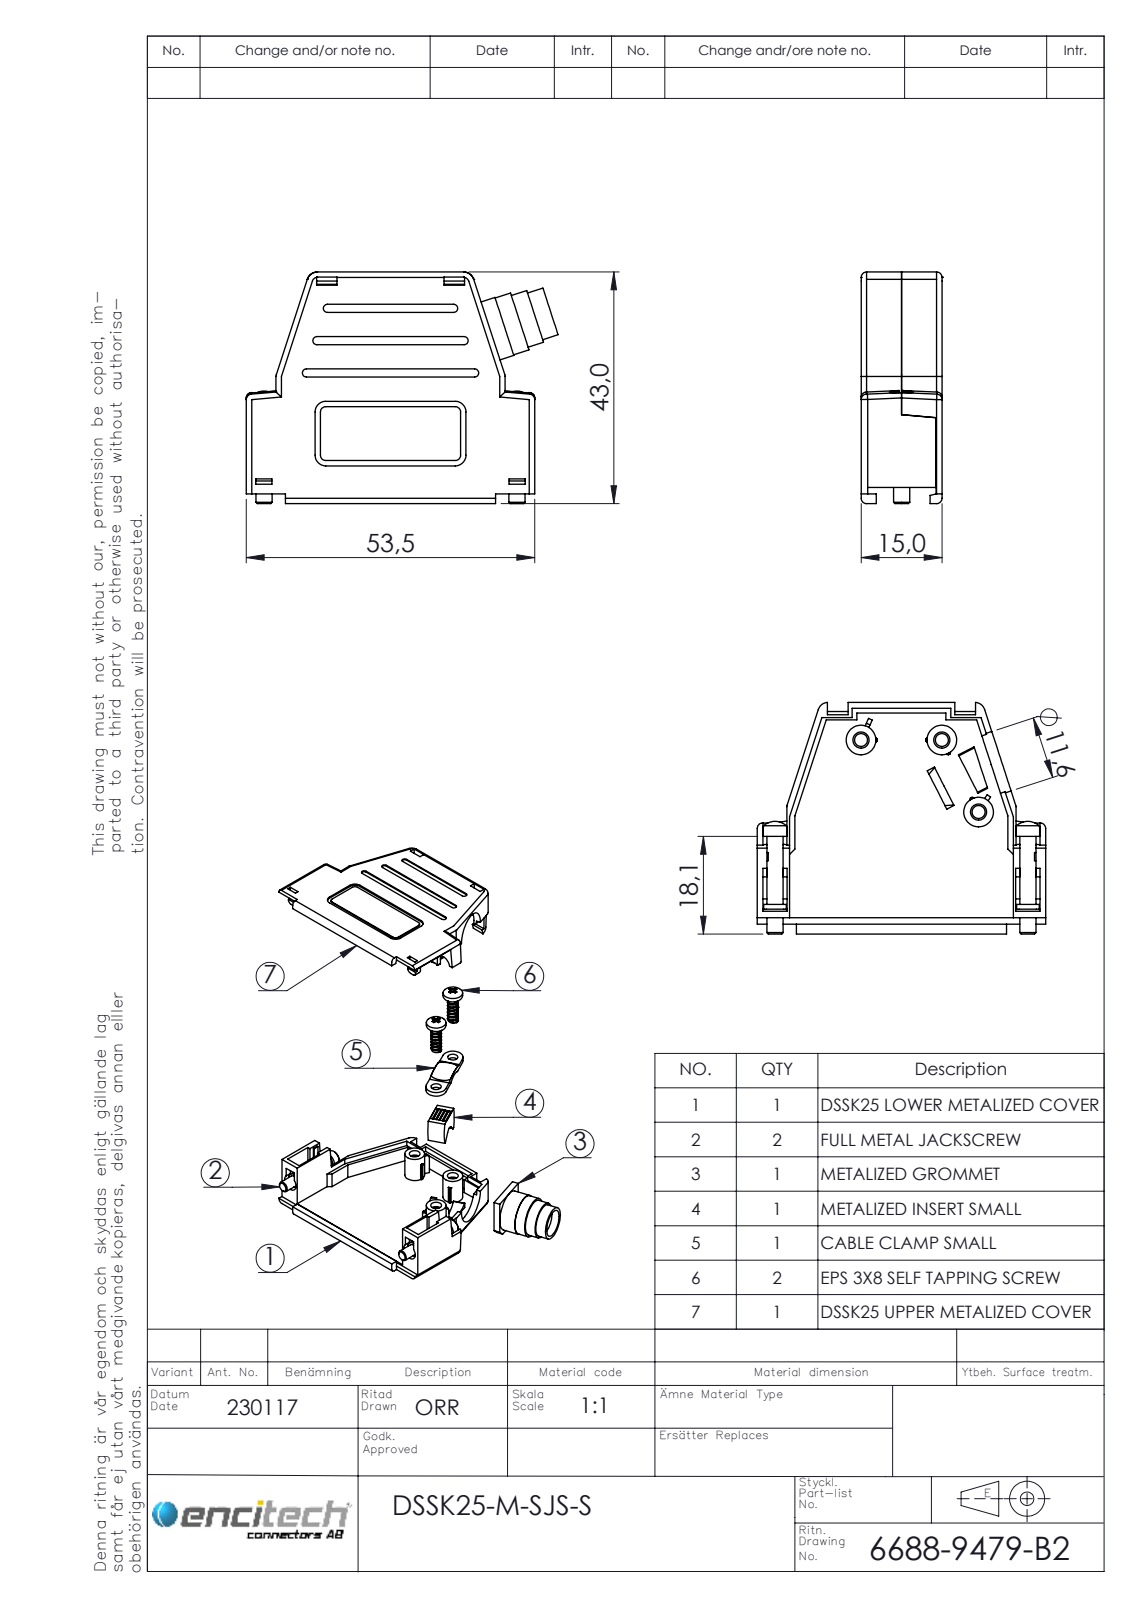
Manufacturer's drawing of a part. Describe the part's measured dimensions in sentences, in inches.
The part is named "6838-0109-32; 6826-0133-01; 6855-0109-01; 6811-0132-05 Part 1 (+4 more)". Its 3-D file was written by "SolidWorks 2021 (AUTOMOTIVE_DESIGN)". It is 11 solids with 758 faces: 482 planar, 216 cylindrical and 60 other. Overall it measures 2.277 by 1.693 by 0.591 inches. Its volume is 0.652 cubic inches and its surface area 24.68 square inches. Round holes: 3 of diameter 0.094, 3 of diameter 0.118, 2 of diameter 0.11, 1 of diameter 0.138, 1 of diameter 0.295, 1 of diameter 0.335, 1 of diameter 0.374, 1 of diameter 0.413, 1 of diameter 0.457. Round bosses or shafts: 3 of diameter 0.217, 2 of diameter 0.215, 2 of diameter 0.173, 2 of diameter 0.165, 2 of diameter 0.118, 2 of diameter 0.097, 1 of diameter 0.445, 1 of diameter 0.437. Partial cylindrical surfaces (rounded edges, fillets, slot ends): 40 of radius 0.039, 14 of radius 0.079, 6 of radius 0.03, 4 of radius 0.004, 4 of radius 0.01, 4 of radius 0.02, 3 of radius 0.228, 2 of radius 0.047. The main face-to-face distances are 0.524, 0.067, 0.457, 0.591, 0.059, 0.079, 0.583, 0.516, 0.228, 0.287. The hole center spacings are 0.591, 0.298, 0.298, 0.744, 1.007.
